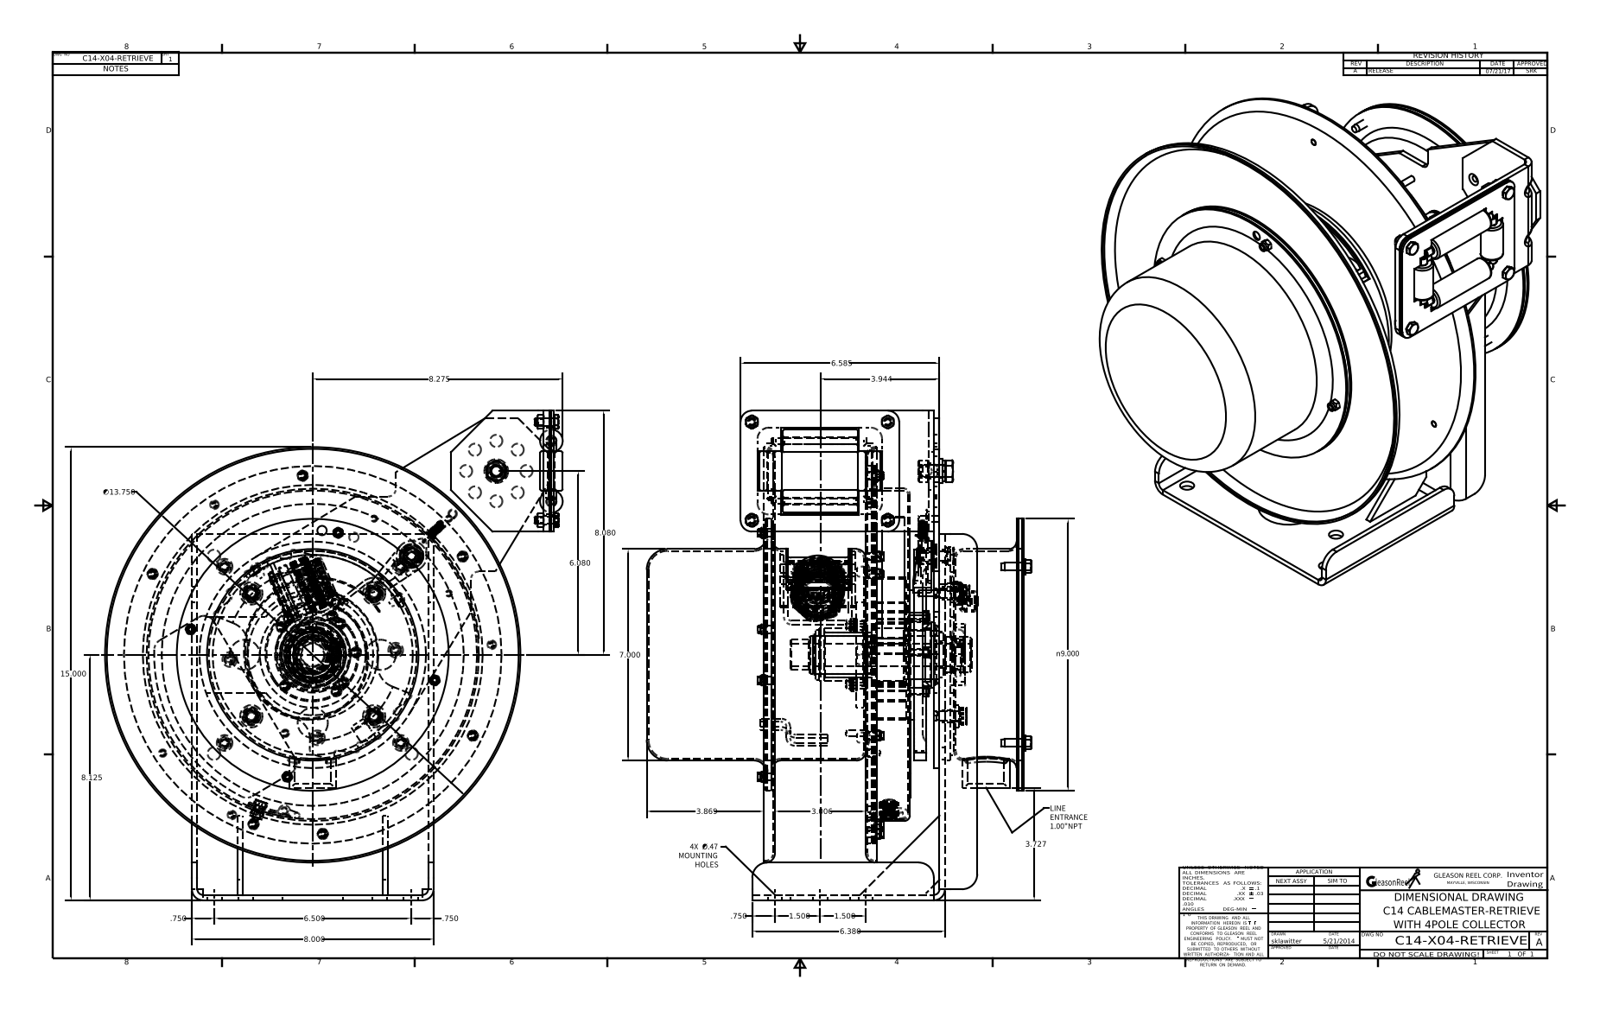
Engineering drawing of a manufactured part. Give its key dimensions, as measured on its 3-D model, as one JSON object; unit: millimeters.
{"part_name": "C14-X04-RETRIEVE (SW)", "step_written_by": "Autodesk Inventor 2016 (AUTOMOTIVE_DESIGN)", "units": "millimeters", "bodies": {"solids": 157, "faces": 3173, "planar": 1254, "cylindrical": 1029, "other": 890}, "overall_size": [411.61, 384.81, 323.2], "volume_mm3": 2658000, "surface_area_mm2": 2232000, "round_holes": [[6.35, 26], [5, 24], [4.13, 19], [10.31, 13], [5.56, 12], [5.41, 8], [10.67, 8], [11.94, 6], [25.4, 6], [4.92, 5], [7.14, 5], [7.98, 5]], "round_bosses_or_shafts": [[5, 24], [6.8, 11], [10, 7], [6, 6], [12.7, 5], [11.6, 5], [8, 5], [19.05, 4]], "partial_cylinders_radius": [[0.76, 67], [0.24, 64], [0.38, 58], [1.98, 18], [0.16, 16], [1.52, 12], [6.35, 8], [9.53, 8]], "face_to_face_distances": [1.52, 3.17, 6.19, 30.93, 126.76, 4.69, 1.5, 4.67, 4.54, 84.04], "hole_center_spacings": [19.44, 25.4, 31.75, 35.92, 46.93, 51.91, 51.93, 76]}
